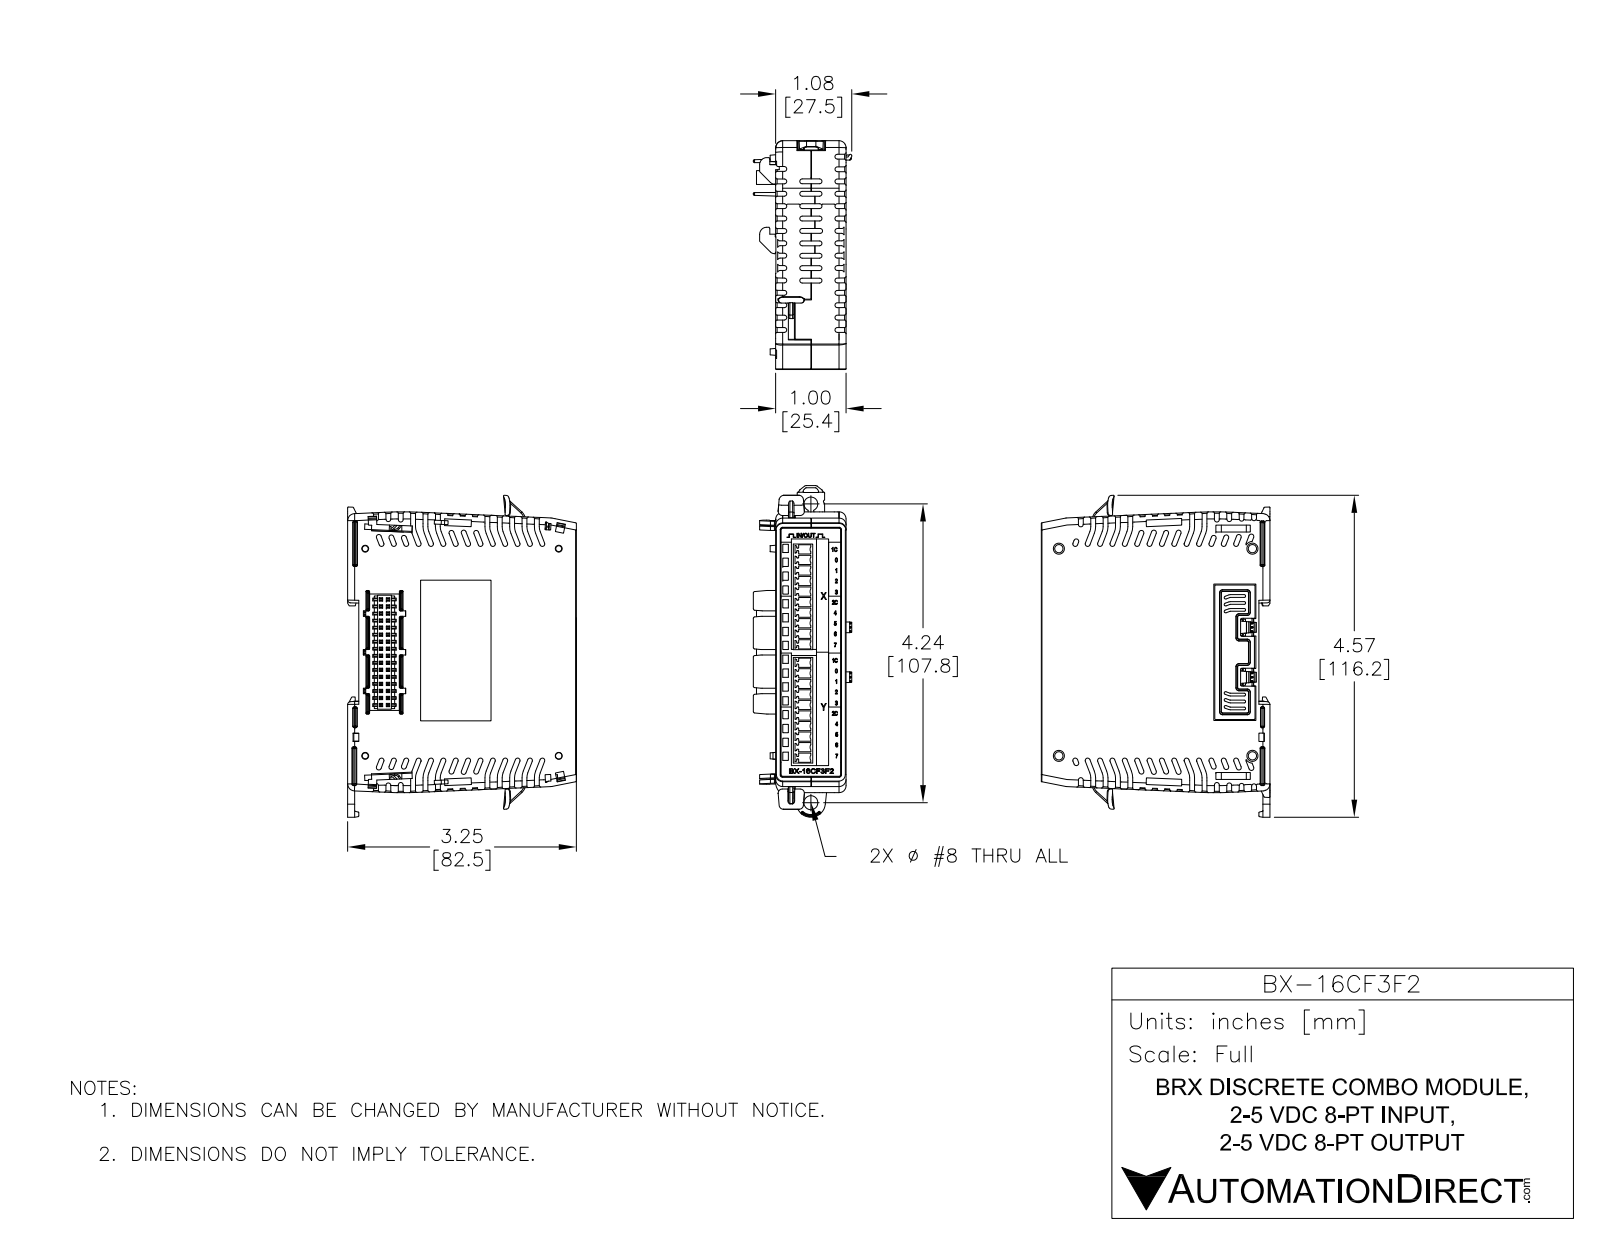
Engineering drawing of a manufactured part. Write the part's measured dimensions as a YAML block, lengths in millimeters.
part_name: "BX-16CF3F2 door mod 1 comb1 fXT c"
step_written_by: "SolidWorks 2017 (AUTOMOTIVE_DESIGN)"
units: millimeters
bodies: {solids: 15, faces: 3853, planar: 2874, cylindrical: 477, other: 502}
overall_size: [116.5, 82.6, 35.6]
volume: 189800
surface_area: 46580
round_holes:
  - {diameter: 1.2, count: 2}
  - {diameter: 1.7, count: 2}
  - {diameter: 3, count: 2}
  - {diameter: 3, count: 2}
  - {diameter: 5.1, count: 1}
round_bosses_or_shafts:
  - {diameter: 1.6, count: 2}
  - {diameter: 1.5, count: 2}
partial_cylinders:
  - {radius: 0.2, count: 101}
  - {radius: 0.3, count: 46}
  - {radius: 0.1, count: 24}
  - {radius: 0.5, count: 22}
  - {radius: 1.6, count: 20}
  - {radius: 3, count: 14}
  - {radius: 1, count: 13}
  - {radius: 0.3, count: 12}
face_to_face_distances: [25.4, 81.6, 81.8, 1, 12.1, 4, 77.5, 77.8, 2.5, 1.3]
hole_center_spacings: [2.5, 20.9, 23.3, 33, 53.2, 55.7, 65.7, 66.5]
